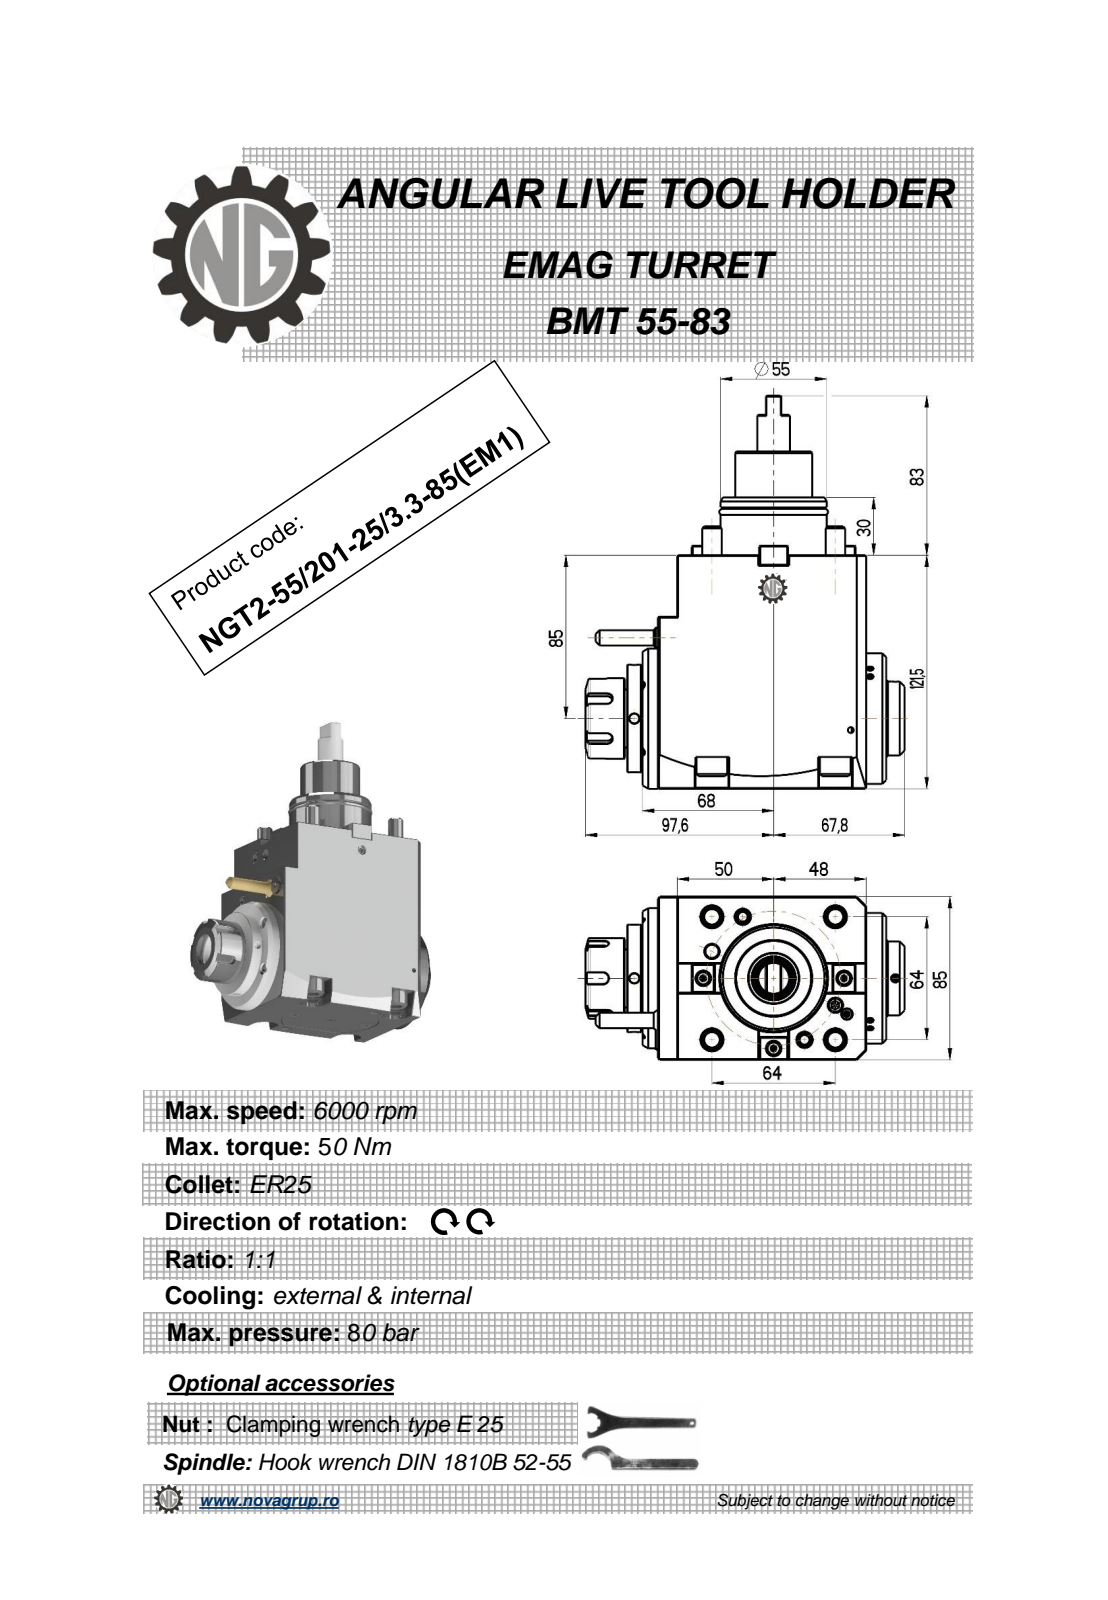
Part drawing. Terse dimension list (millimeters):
name: NGT2_55_201_25_3_3_85_EM1
written by: PRO/ENGINEER BY PARAMETRIC TECHNOLOGY CORPORATION, 2010280 (CONFIG_CONTROL_DESIGN)
unit: mm
bodies: 2 solids, 489 faces (229 planar, 111 cylindrical, 149 other)
size: 204.5 × 165.4 × 85
volume: 1 297 000 mm³; area: 111 652 mm²
holes: 3× ⌀5, 2× ⌀6.8, 1× ⌀3, 1× ⌀12
bosses: 4× ⌀16, 4× ⌀10, 1× ⌀73, 1× ⌀68, 1× ⌀56, 1× ⌀55, 1× ⌀50, 1× ⌀43.4
rounds: 20× R0.32, 6× R0.22, 5× R3, 4× R8.5, 2× R0.8, 2× R480
face distances: 85, 121.5, 8, 10, 108, 98, 18, 116, 108.3, 16
hole spacings: 42.62, 69.86, 105.19
